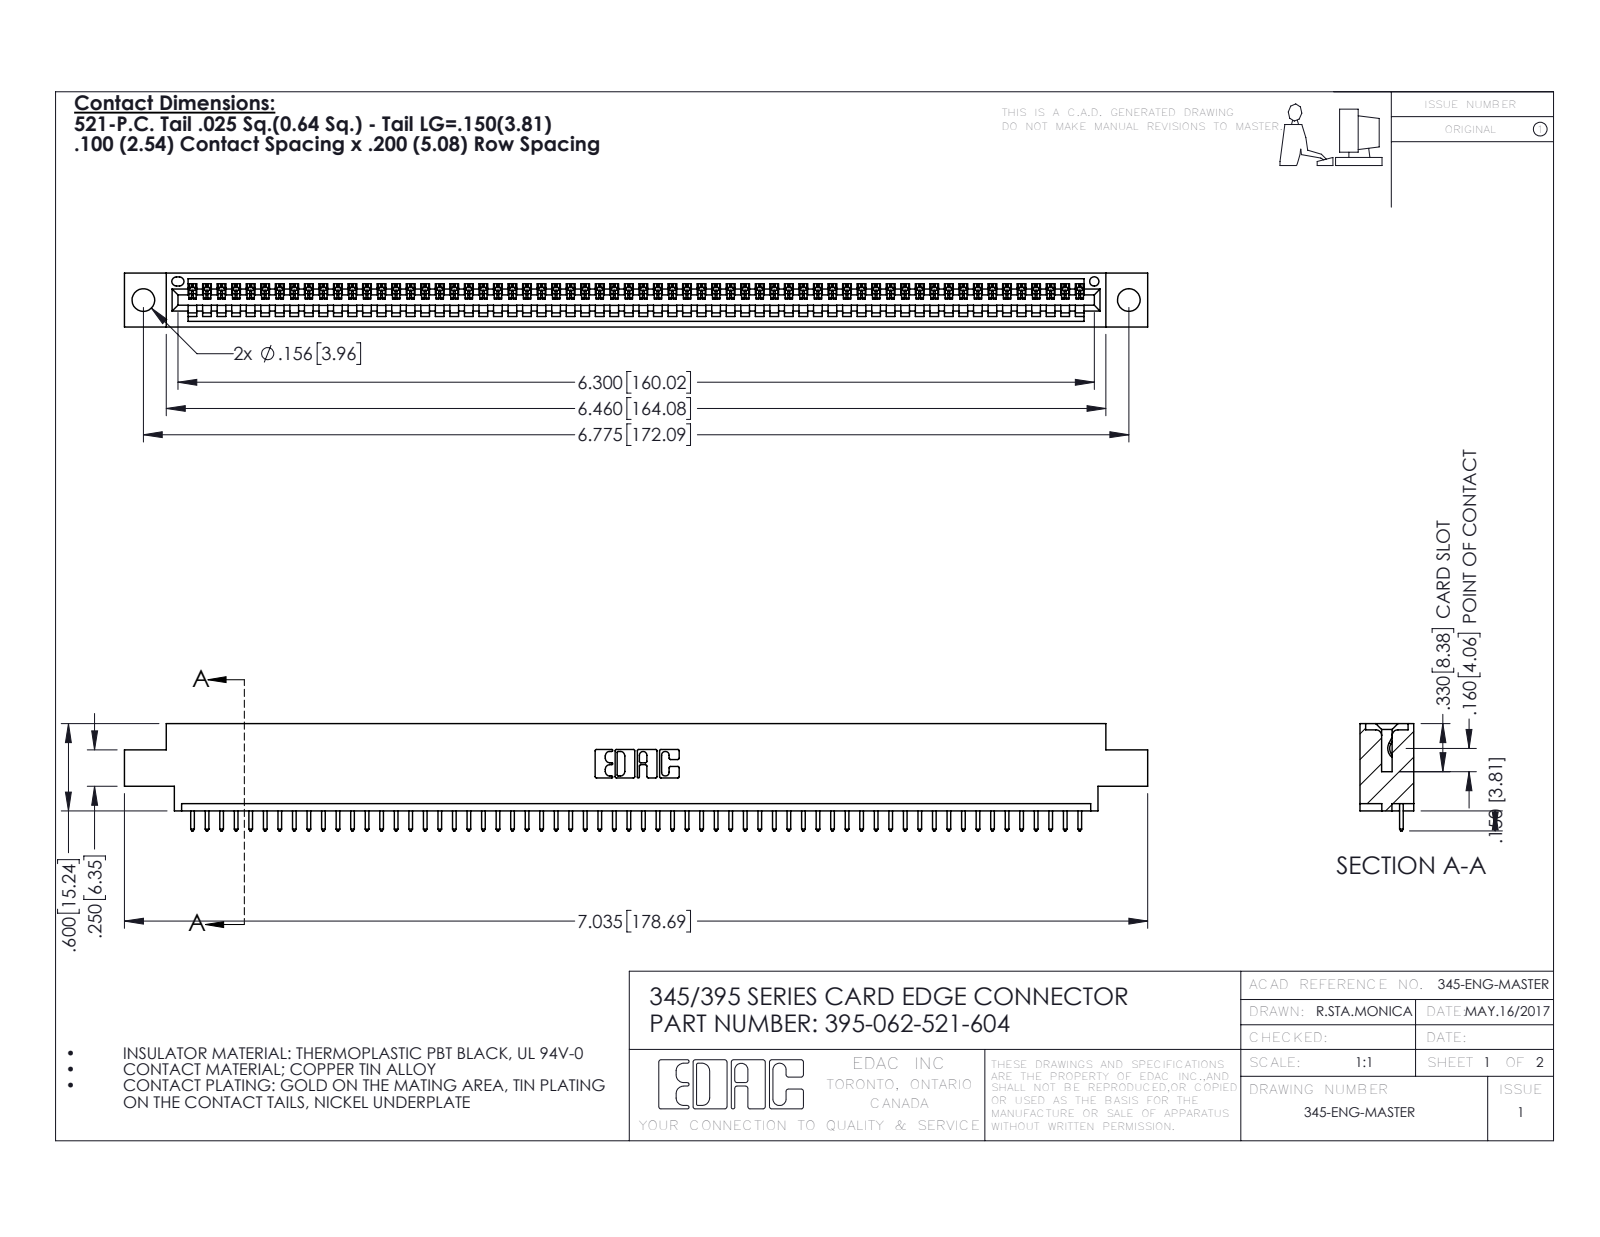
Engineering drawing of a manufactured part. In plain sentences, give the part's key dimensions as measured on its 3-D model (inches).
The part is named "395-062-521-604; 345 Part_0.170 Offset - 0.156 Dia-TH; 345-292-001_345-293-121". Its 3-D file was written by "SolidWorks 2016 (CONFIG_CONTROL_DESIGN)". It is 63 solids with 3726 faces: 2564 planar, 1162 cylindrical and 0 other. Overall it measures 7.035 by 0.737 by 0.37 inches. Its volume is 1.023 cubic inches and its surface area 33.77 square inches. Round holes: 2 of diameter 0.156, 1 of diameter 0.064. Partial cylindrical surfaces (rounded edges, fillets, slot ends): 124 of radius 0.006, 124 of radius 0.01, 22 of radius 0.01, 6 of radius 0.007, 6 of radius 0.031, 3 of radius 0.026, 2 of radius 0.031, 2 of radius 0.04. The main face-to-face distances are 0.298, 0.072, 0.37, 0.2, 0.098, 0.272, 0.025, 0.225, 0.175, 0.149. The hole center spacings are 0.27, 6.539, 6.775.
